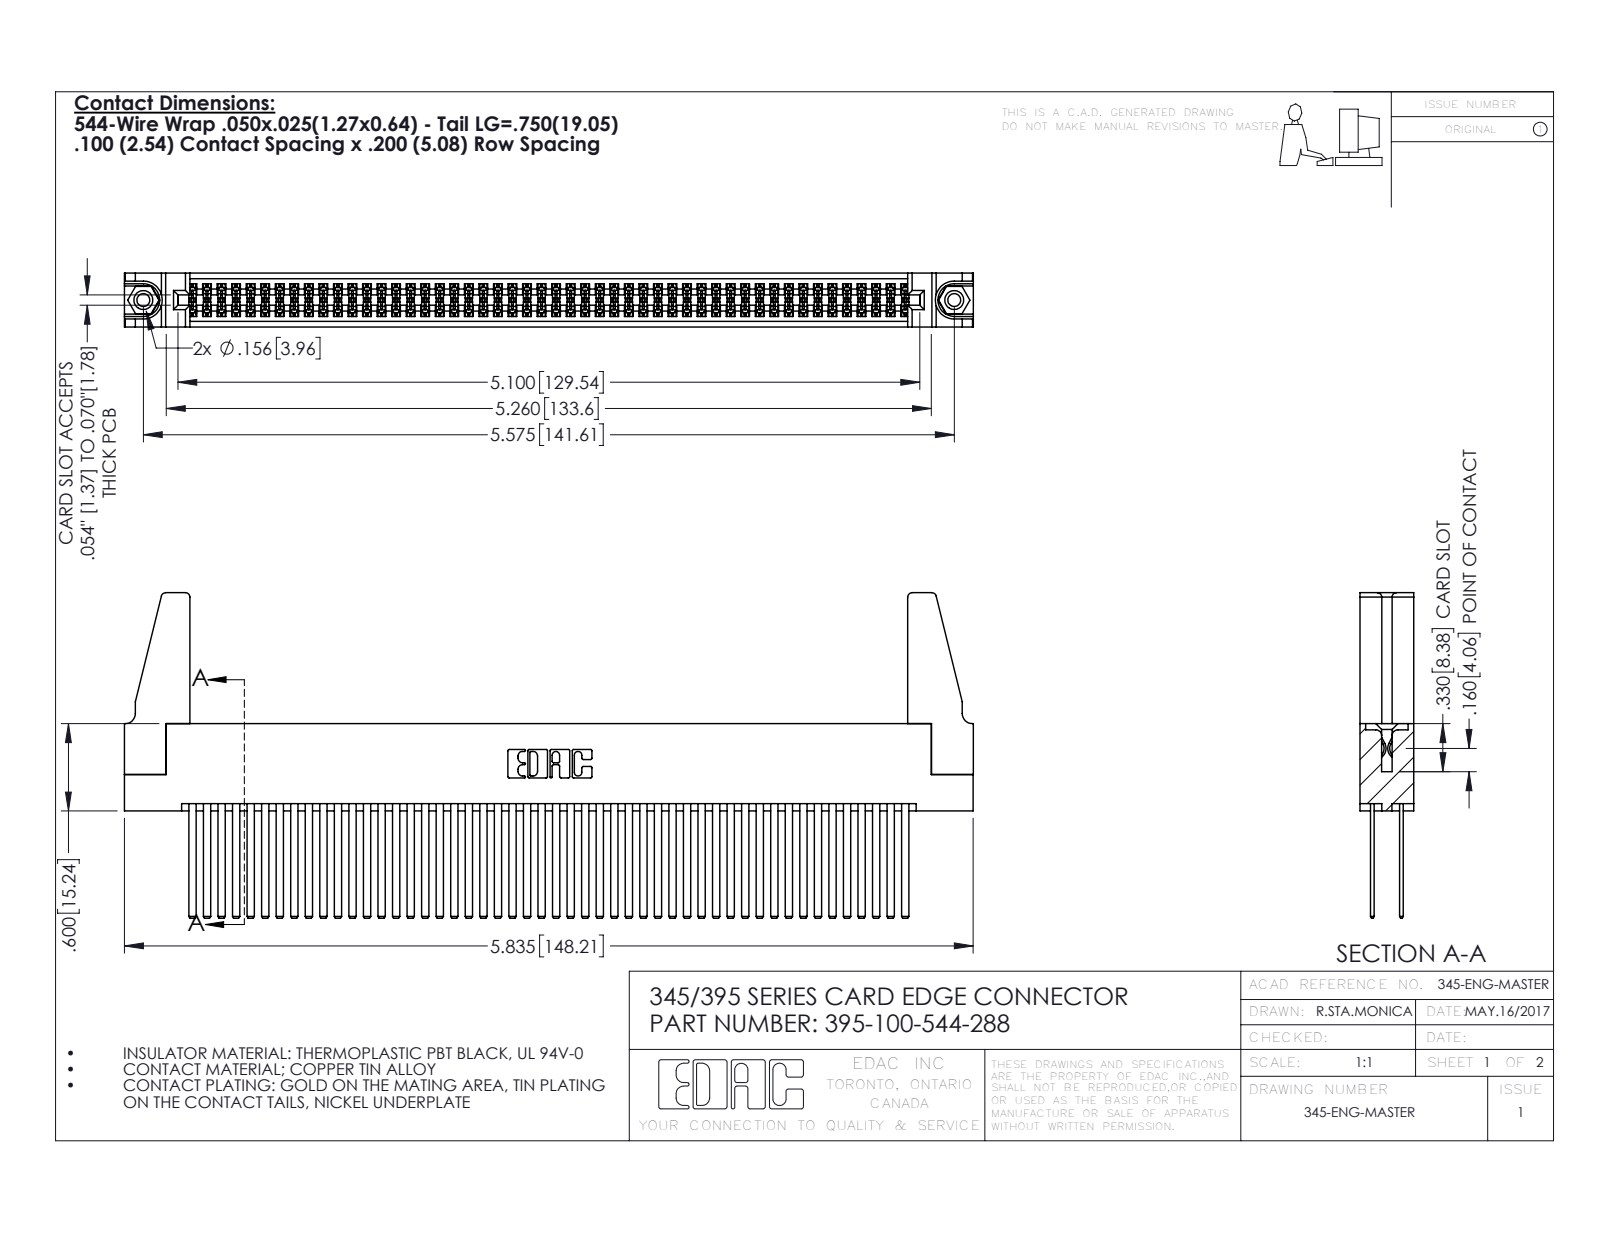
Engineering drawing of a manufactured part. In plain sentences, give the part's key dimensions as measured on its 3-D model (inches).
The part is named "395-100-544-288; 345-220-078_345-220-088; 345-250-001_345-250-001-102; 345 Part_Flush Mounting Lugs - 0.156 Dia-TH (+1 more)". Its 3-D file was written by "SolidWorks 2016 (CONFIG_CONTROL_DESIGN)". It is 105 solids with 4650 faces: 3052 planar, 1582 cylindrical and 16 other. Overall it measures 5.836 by 2.237 by 0.37 inches. Its volume is 1.167 cubic inches and its surface area 47.82 square inches. Round holes: 2 of diameter 0.089, 2 of diameter 0.125, 2 of diameter 0.156, 1 of diameter 0.064. Round bosses or shafts: 2 of diameter 0.155. Partial cylindrical surfaces (rounded edges, fillets, slot ends): 150 of radius 0.006, 22 of radius 0.01, 8 of radius 0.03, 6 of radius 0.007, 6 of radius 0.031, 3 of radius 0.026, 2 of radius 0.014, 2 of radius 0.019. The main face-to-face distances are 0.072, 0.298, 0.2, 0.098, 0.272, 0.025, 0.225, 0.37, 0.175, 0.149. The hole center spacings are 0.27, 5.339, 5.575.
